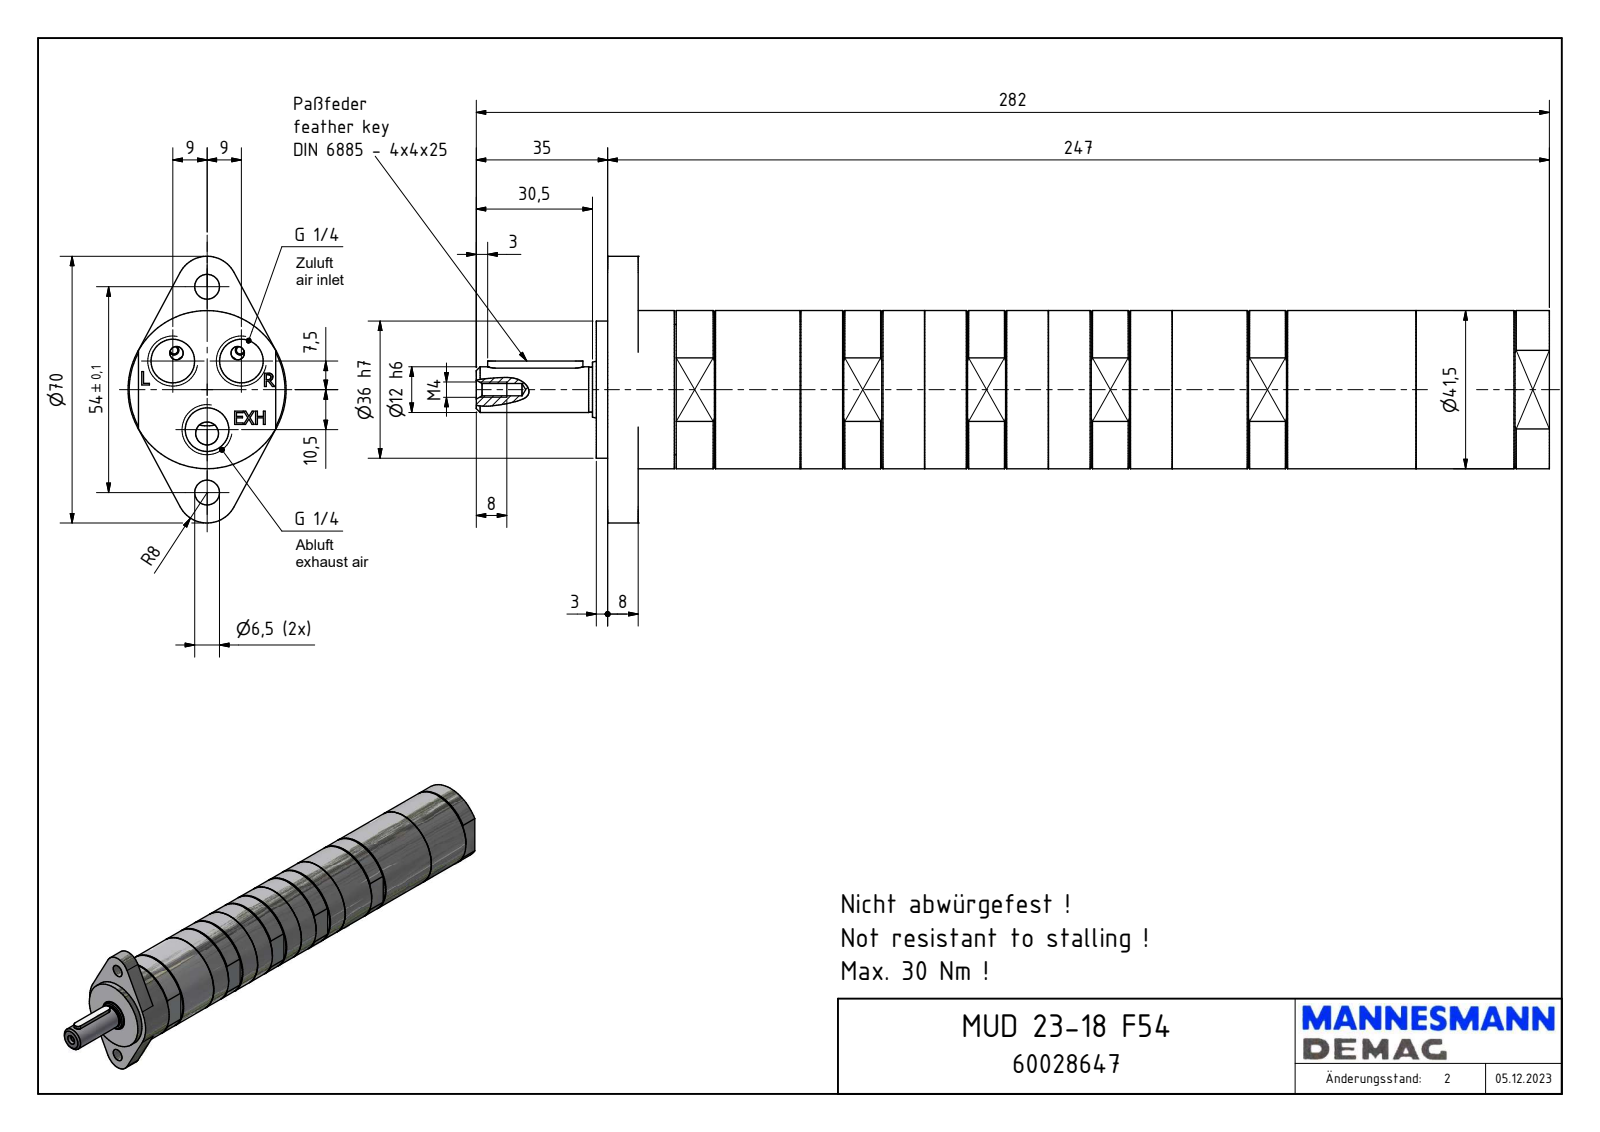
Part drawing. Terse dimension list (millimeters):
name: MUD 23-18 F54_60028647
written by: Autodesk Inventor 2024 (AUTOMOTIVE_DESIGN)
unit: mm
bodies: 1 solid, 200 faces (113 planar, 40 cylindrical, 47 other)
size: 281.7 × 70 × 41.5
volume: 339 093 mm³; area: 40 766 mm²
holes: 3× ⌀11.45, 2× ⌀6.5, 1× ⌀3.24, 1× ⌀16
bosses: 1× ⌀41.5, 1× ⌀37.99, 1× ⌀36, 1× ⌀14.95, 1× ⌀12, 1× ⌀11.8
rounds: 2× R2, 2× R8
face distances: 247.2, 38, 3, 250.2, 10, 11, 8, 239.2, 229.2, 1
hole spacings: 11.72, 20.12, 21.48, 27, 35.65, 10.5, 16.5, 18
